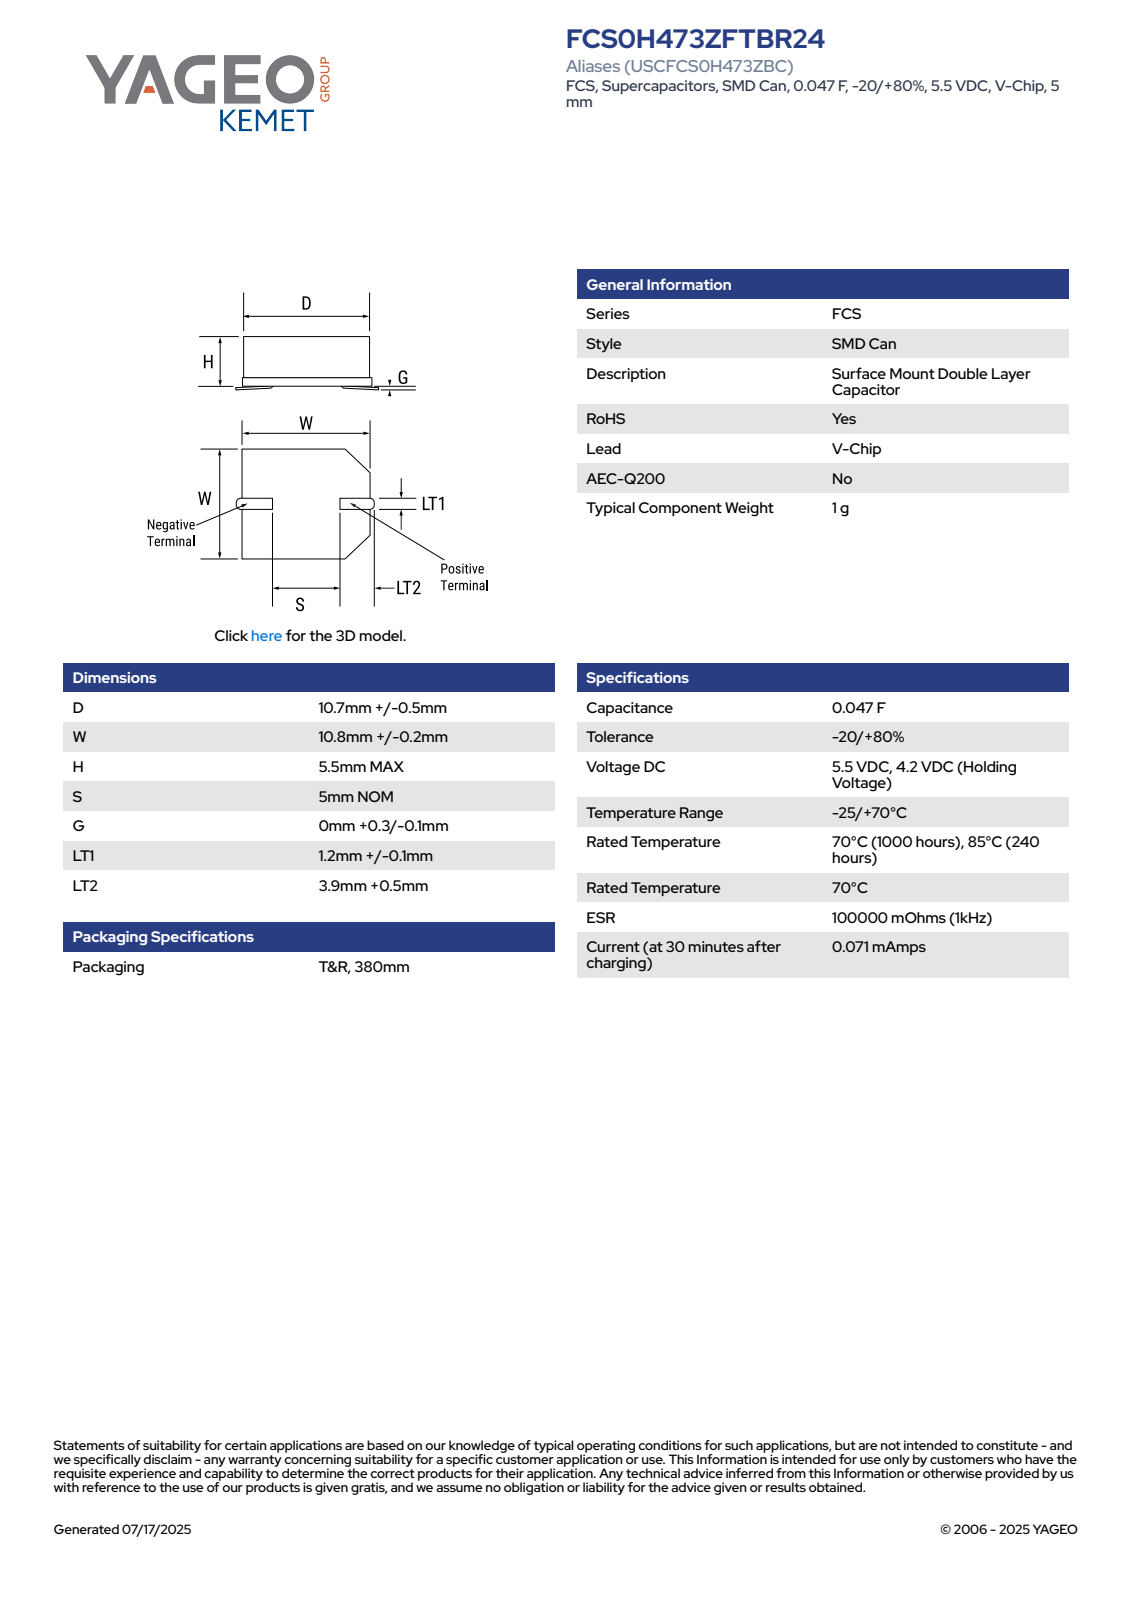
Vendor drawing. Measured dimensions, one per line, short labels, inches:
name: CDC_VC_D10.7L5.5LT11.3G0.3W11LT24.4
written by: SolidWorks 2014 (AUTOMOTIVE_DESIGN)
unit: in
bodies: 5 solids, 60 faces (49 planar, 5 cylindrical, 6 other)
size: 0.543 × 0.433 × 0.217
volume: 0.031 in³; area: 0.963 in²
bosses: 1× ⌀0.421
rounds: 2× R0.008, 1× R0.167
face distances: 0.054, 0.205, 0.15, 0.433, 0.217, 0.066, 0.191, 0.242, 0.051, 0.055
